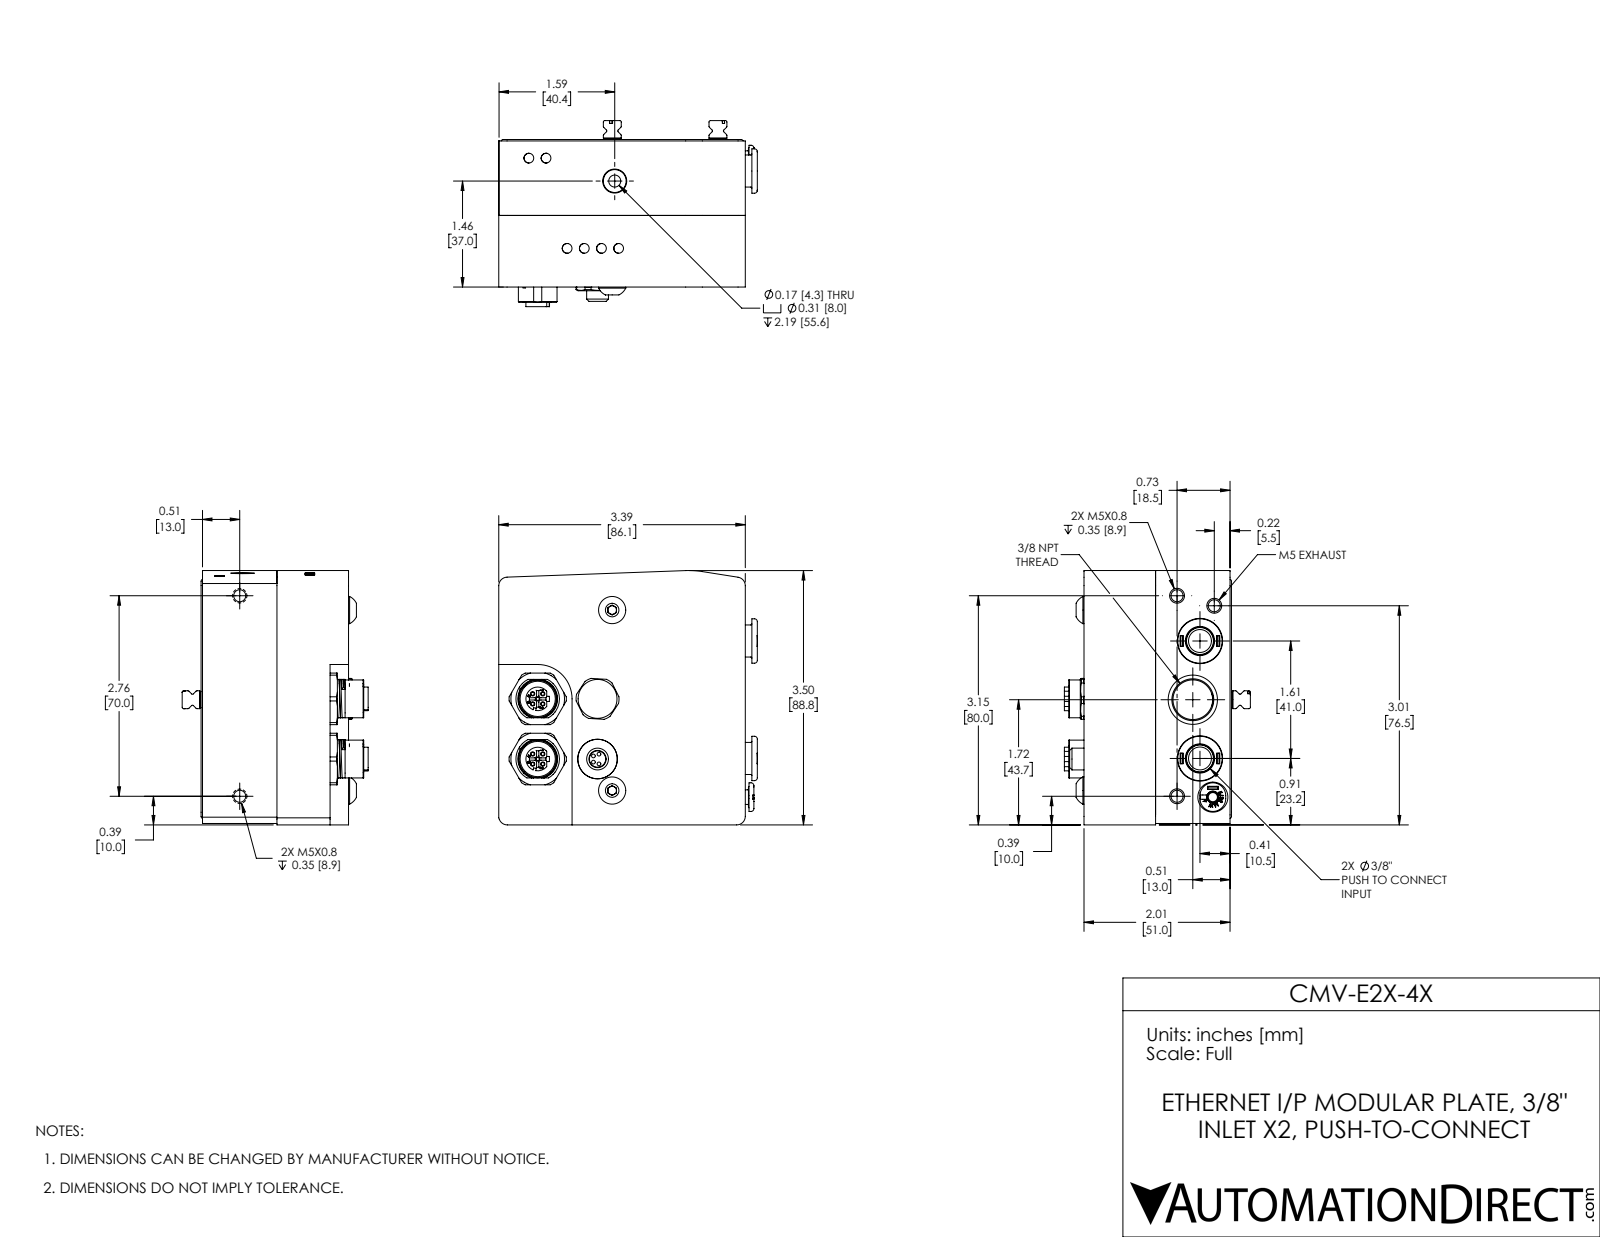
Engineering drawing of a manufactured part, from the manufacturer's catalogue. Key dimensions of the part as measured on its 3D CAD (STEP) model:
Part name (STEP PRODUCT): CMV-E2X-4X
STEP written by: SolidWorks 2017 (AUTOMOTIVE_DESIGN)
Units: millimetres
Bodies: 21 solids, 2240 faces (860 planar, 680 cylindrical, 700 other)
Overall size (bounding box): 90.3 × 88.8 × 64.95
Volume: 362 015 mm³ · Surface area: 67 395 mm²
Round holes (diameter × count): ⌀1.1 ×10, ⌀4.2 ×8, ⌀3.4 ×6, ⌀8 ×3, ⌀11.9 ×3, ⌀13.8 ×3, ⌀5.5 ×2, ⌀8.8 ×2, ⌀9.7 ×2, ⌀10.2 ×2, ⌀11 ×2, ⌀11.3 ×2
Round bosses / shafts (diameter × count): ⌀1.5 ×4, ⌀1.3 ×4, ⌀0.98 ×4, ⌀0.5 ×4, ⌀15.5 ×2, ⌀13.5 ×2, ⌀11.6 ×2, ⌀11.2 ×2
Partial cylindrical surfaces — rounded edges, fillets, slot ends (radius × count): R0.1 ×120, R0.85 ×40, R0.2 ×36, R0.8 ×8, R3 ×8, R0.6 ×4, R2.3 ×4, R0.5 ×2
Main face-to-face distances: 26, 25, 51, 86, 0.5, 86.1, 1, 44.55, 18.55, 6.45
Hole centre spacings: 2.5, 3.54, 21, 5.01, 19.21, 19.31, 21.3, 22.74
